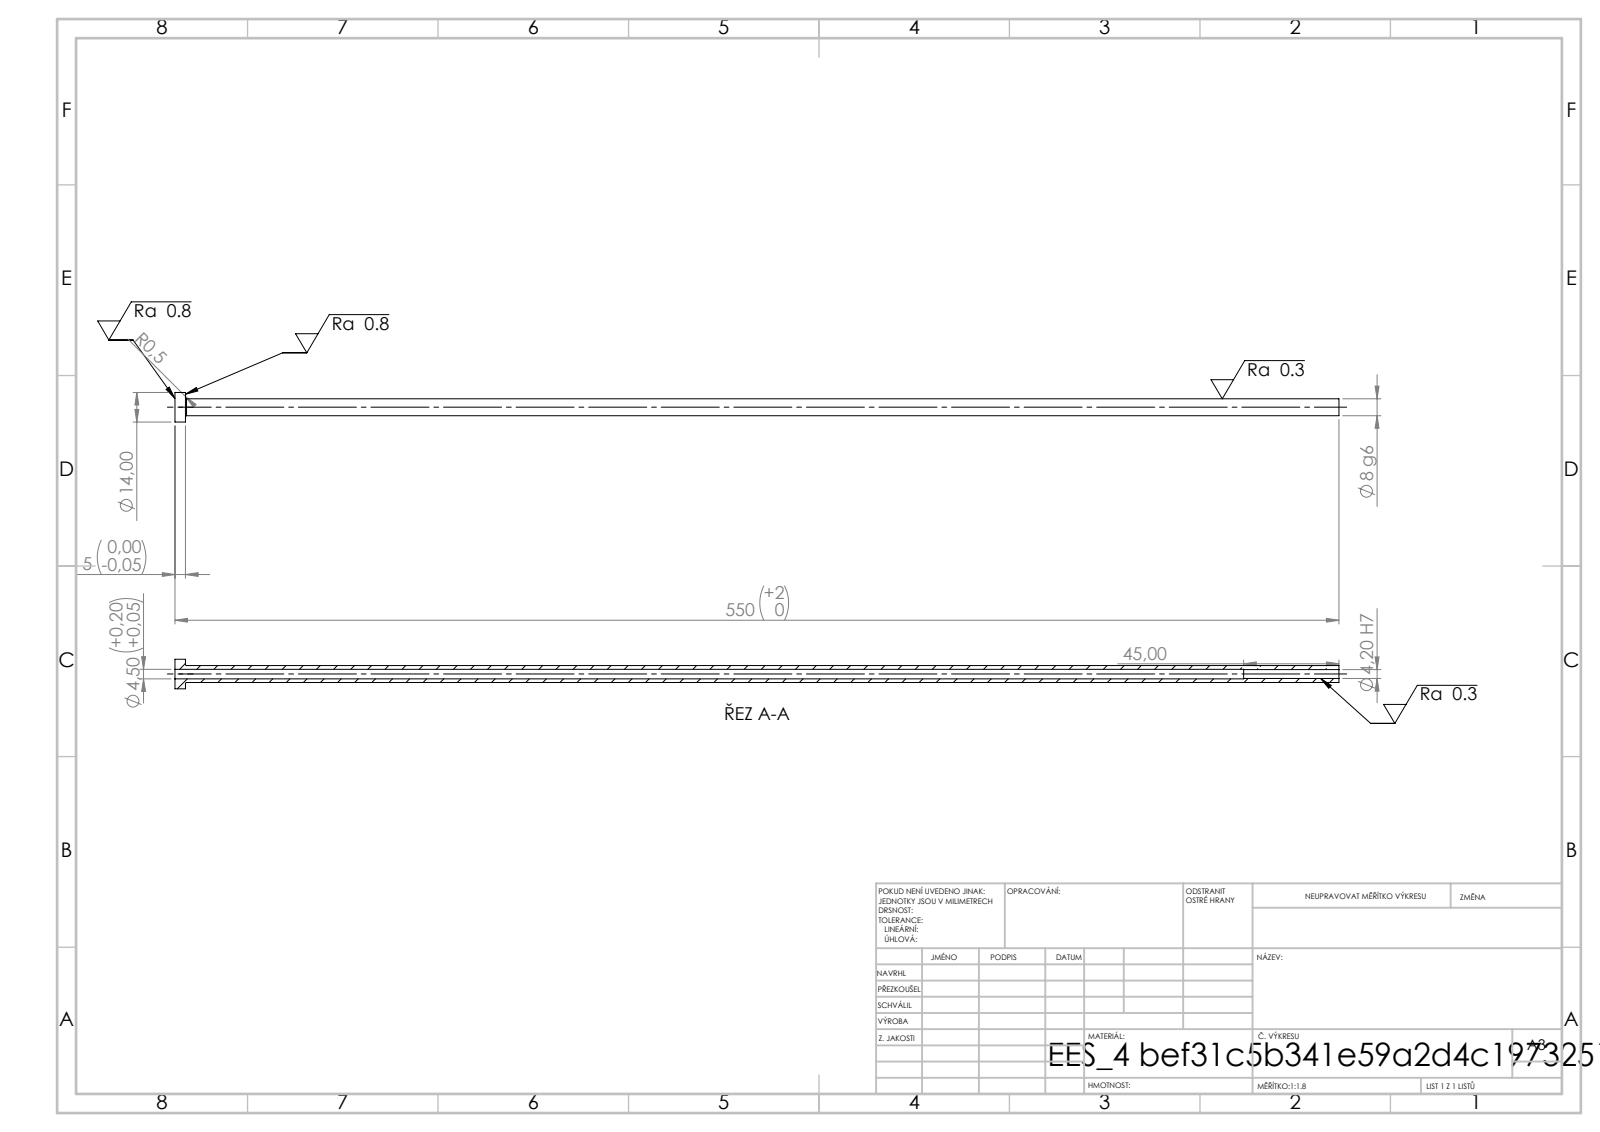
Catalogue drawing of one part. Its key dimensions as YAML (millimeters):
step_written_by: "SolidWorks 2019 (CONFIG_CONTROL_DESIGN)"
units: millimeters
bodies: {solids: 1, faces: 14, planar: 4, cylindrical: 8, other: 2}
overall_size: [550, 14, 14]
volume: 19511
surface_area: 21925
round_holes:
  - {diameter: 4.2, count: 1}
  - {diameter: 4.5, count: 1}
round_bosses_or_shafts:
  - {diameter: 14, count: 1}
  - {diameter: 8, count: 1}
face_to_face_distances: [5, 550, 545, 505, 500, 45]
